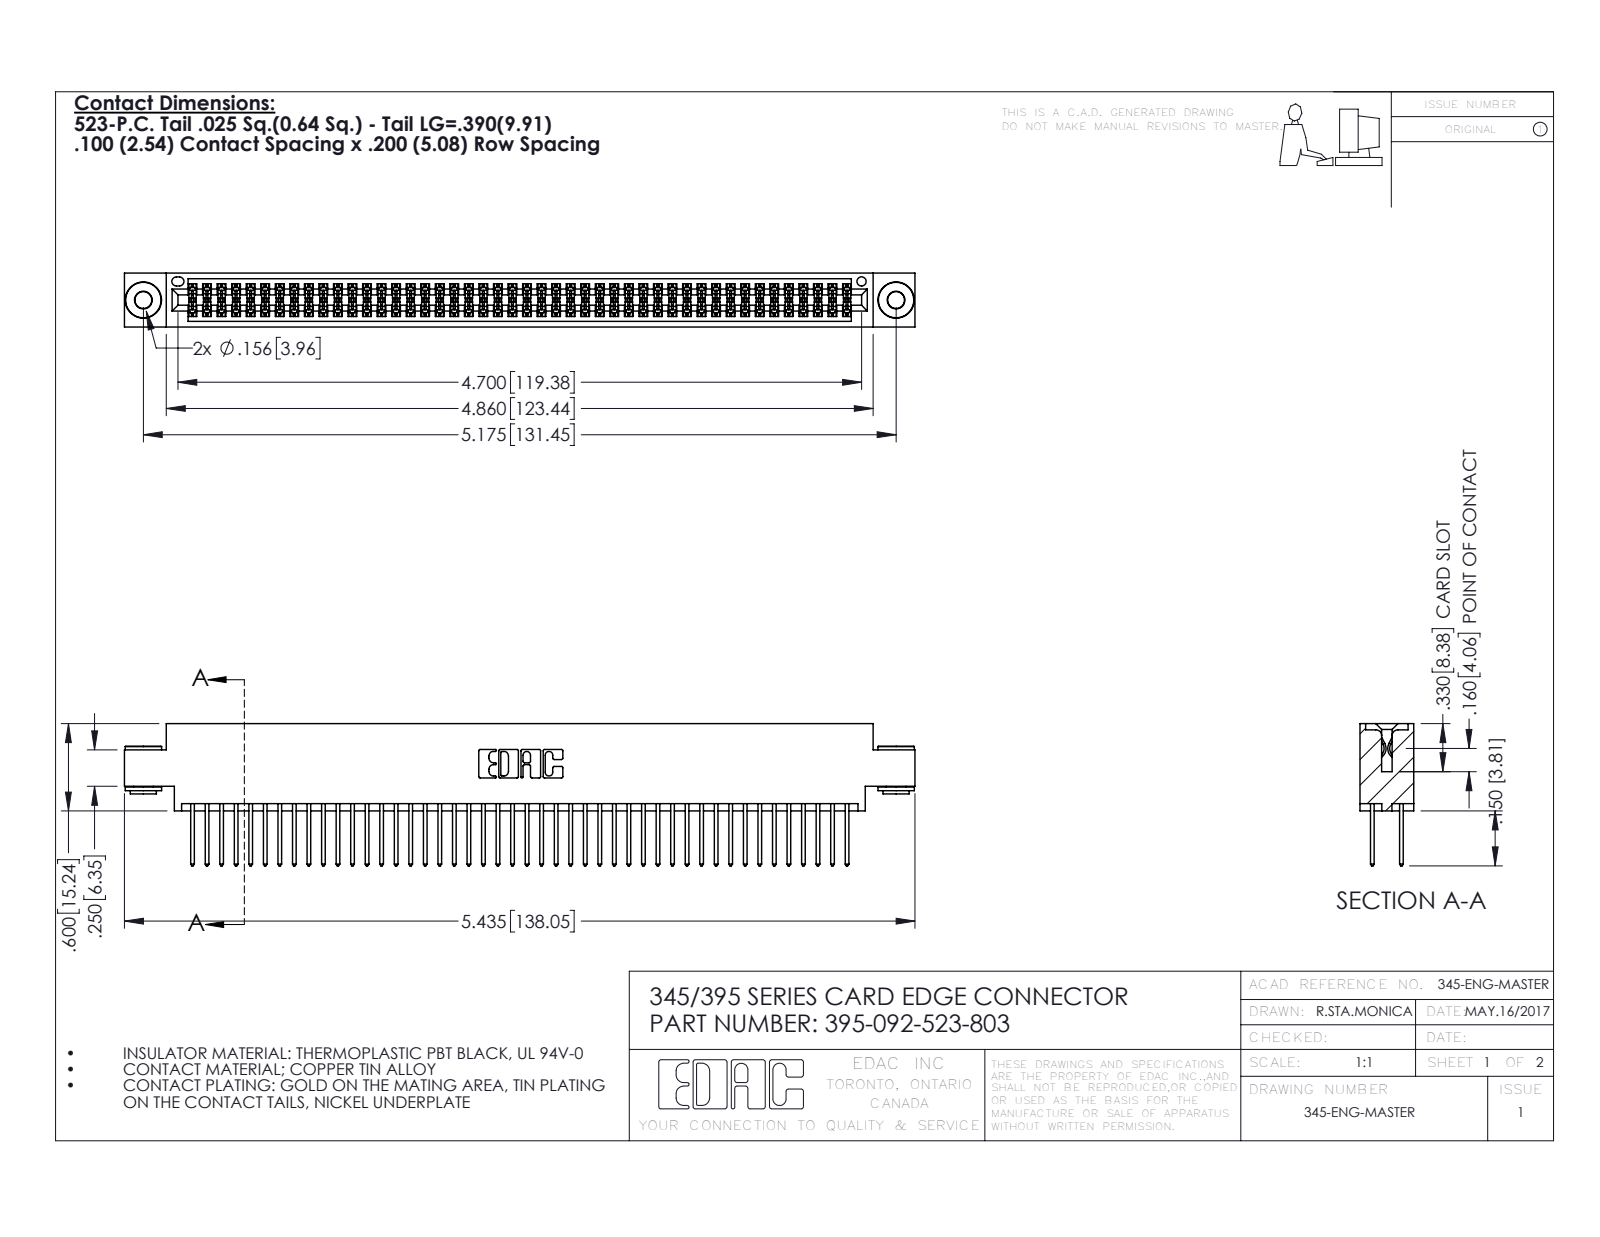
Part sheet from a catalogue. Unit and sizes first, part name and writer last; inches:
Units: inches
Overall size (bounding box): 5.435 × 0.977 × 0.37
Round holes (diameter × count): ⌀0.116 ×2, ⌀0.156 ×2, ⌀0.064 ×1
Round bosses / shafts (diameter × count): ⌀0.25 ×2, ⌀0.18 ×2, ⌀0.136 ×2
Partial cylindrical surfaces — rounded edges, fillets, slot ends (radius × count): R0.006 ×138, R0.01 ×92, R0.01 ×22, R0.007 ×6, R0.031 ×6, R0.026 ×3, R0.014 ×2, R0.019 ×2
Main face-to-face distances: 0.072, 0.298, 0.2, 0.098, 0.272, 0.025, 0.37, 0.225, 0.175, 0.149
Hole centre spacings: 0.27, 4.939, 5.175
Volume: 0.826 in³ · Surface area: 33 in²
Bodies: 95 solids, 4768 faces (3130 planar, 1630 cylindrical, 8 other)
Part name (STEP PRODUCT): 345 Part_0.170 Offset - 0.156 Dia-TH; 395-092-523-803; 345-250-002_345-250-002-102; 345-292-001_345-293-123
STEP written by: SolidWorks 2016 (CONFIG_CONTROL_DESIGN)
